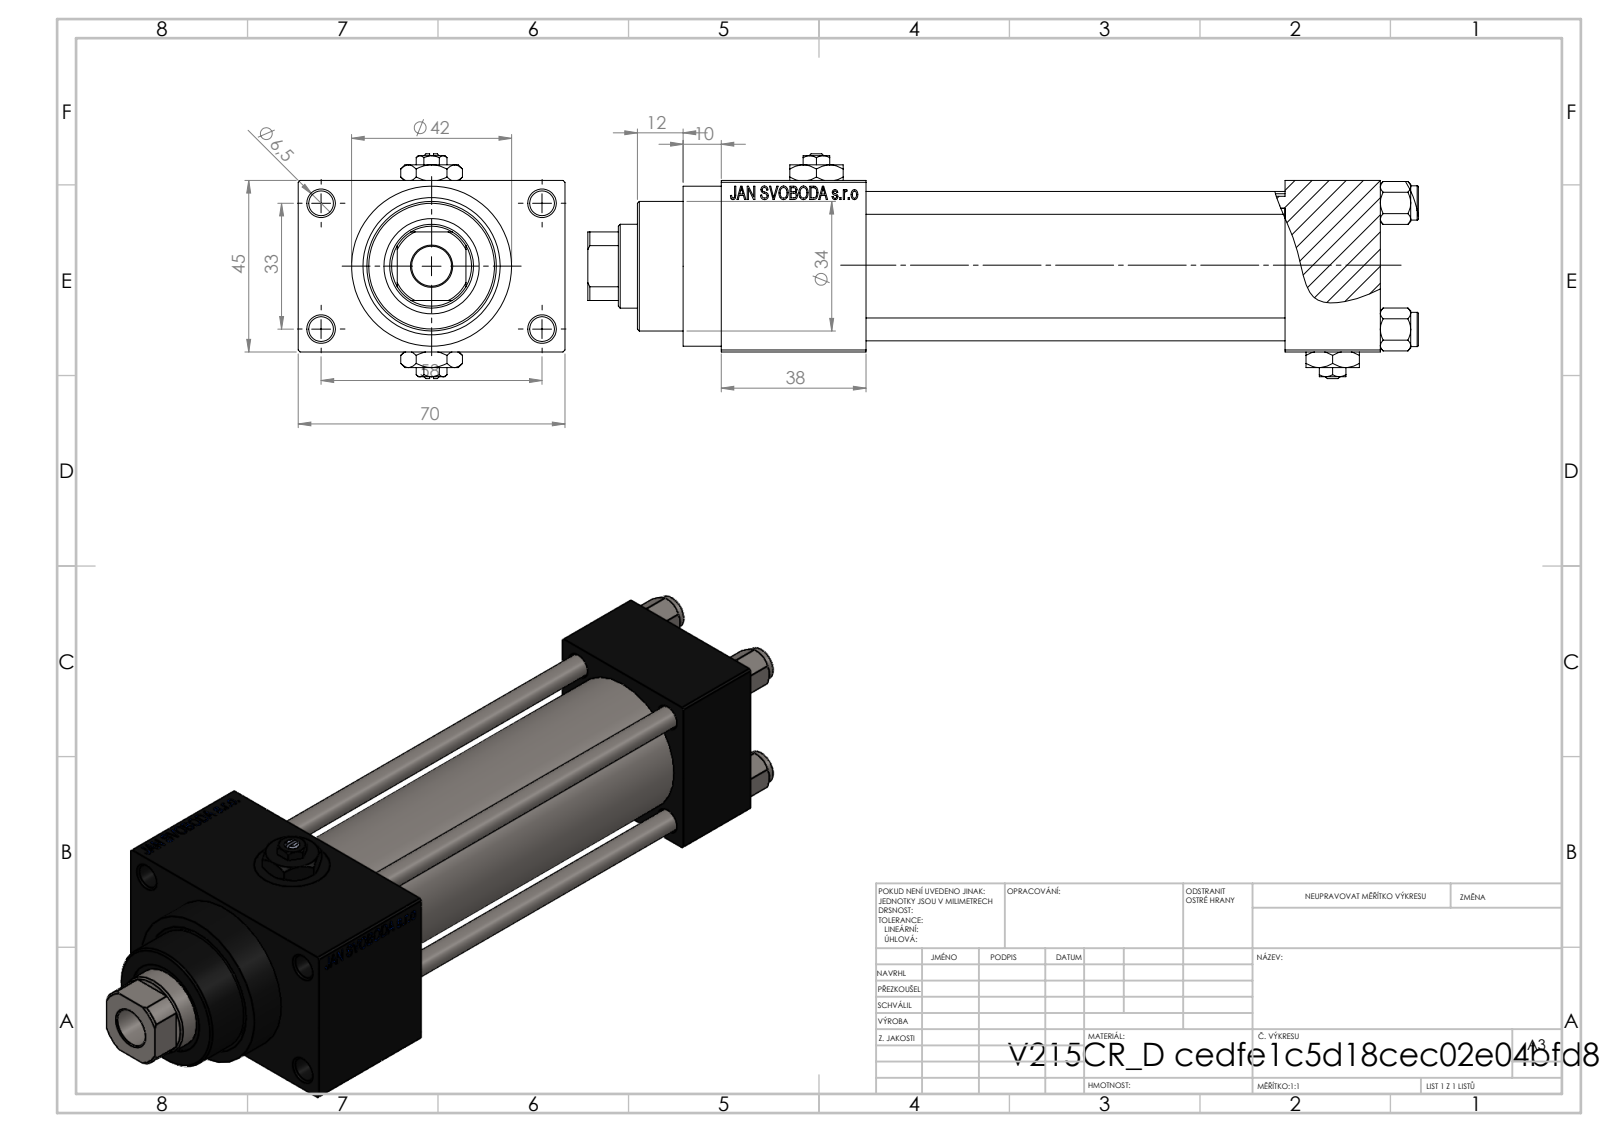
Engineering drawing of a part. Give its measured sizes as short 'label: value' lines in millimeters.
name: NUT_M5_D; V215CR_VCP_D; V215_VC_A; V215CR_D_Body (+2 more)
written by: SolidWorks 2019 (CONFIG_CONTROL_DESIGN)
unit: mm
bodies: 13 solids, 1189 faces (540 planar, 89 cylindrical, 560 other)
size: 218 × 70 × 59
volume: 295 531 mm³; area: 102 423 mm²
holes: 4× ⌀6, 4× ⌀6.5, 2× ⌀7, 2× ⌀13.16, 2× ⌀20, 1× ⌀10.5, 1× ⌀22, 1× ⌀24, 1× ⌀25, 1× ⌀32, 1× ⌀33
bosses: 4× ⌀9, 1× ⌀42, 1× ⌀38, 1× ⌀34
rounds: 1× R10.5
face distances: 45, 25, 12.5, 57.5, 110, 135, 148, 38, 70, 173
hole spacings: 12.4, 23.48, 33.2, 33.37, 35.35, 45.6, 56.35, 33
